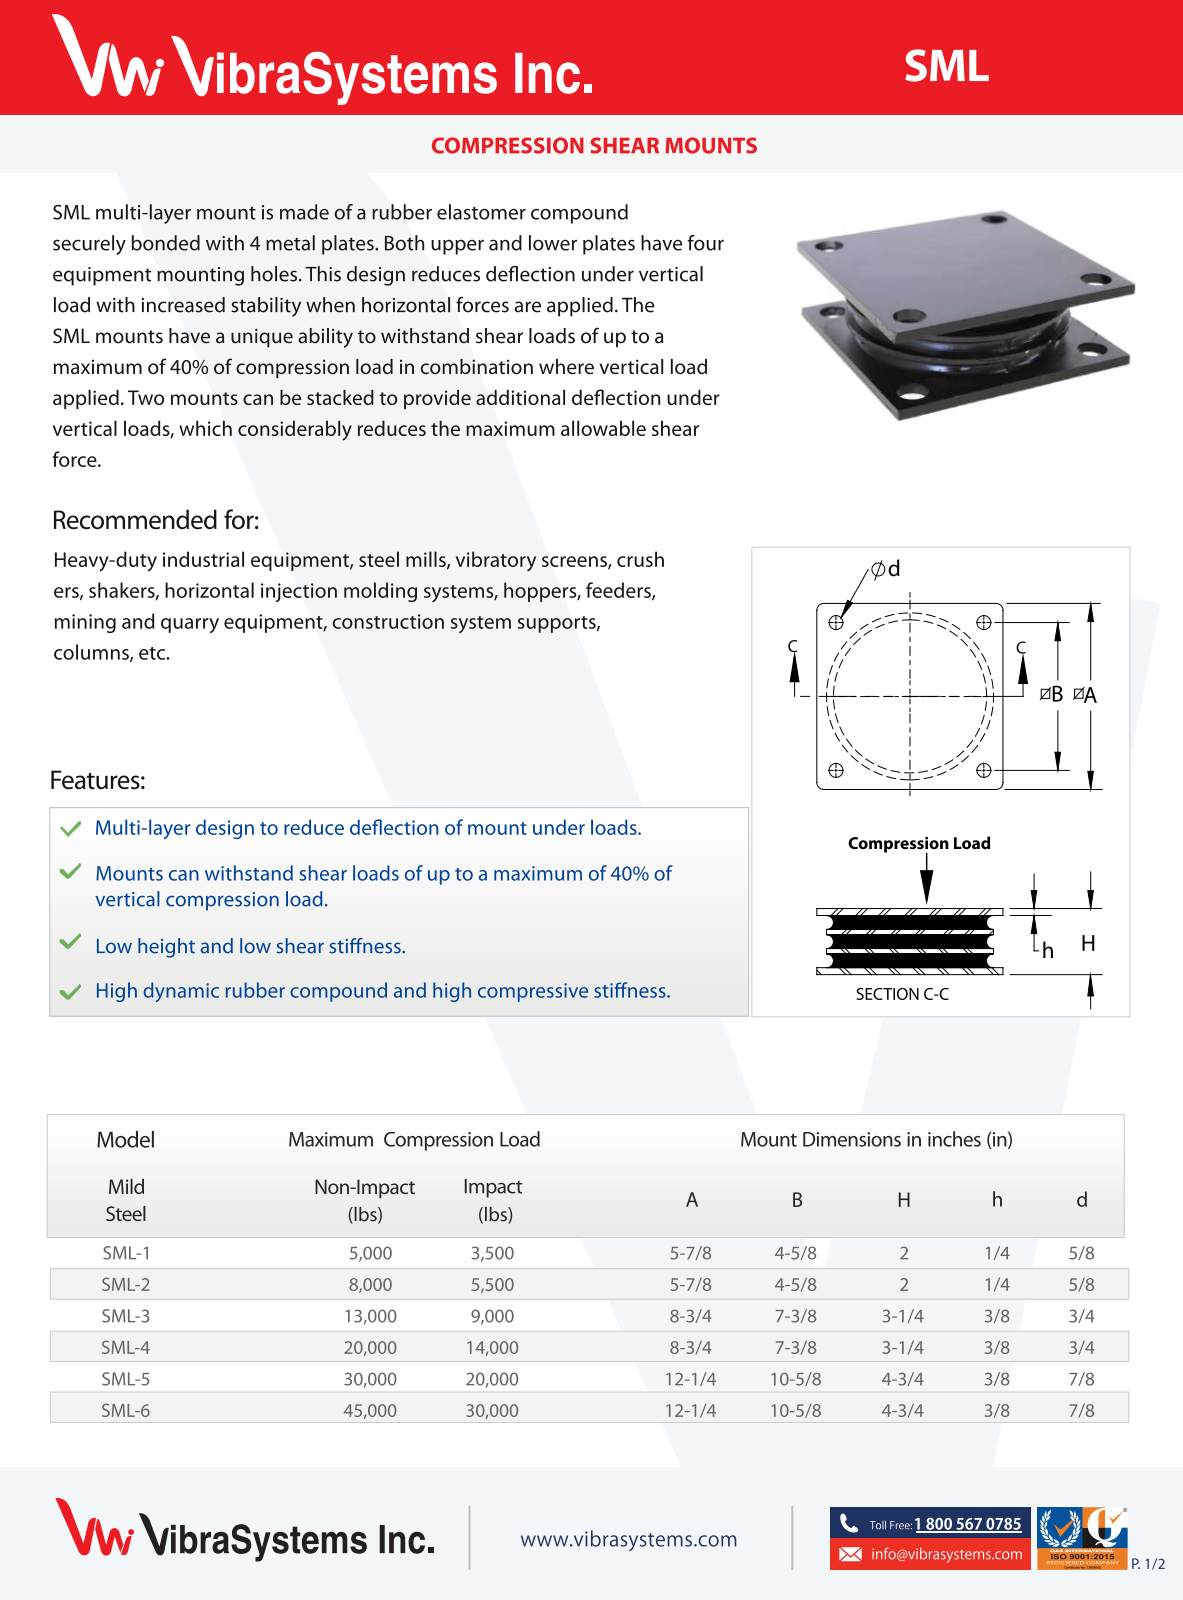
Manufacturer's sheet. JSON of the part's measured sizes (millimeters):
{"part_name": "SML-6 RevF", "step_written_by": "SolidWorks 2016 (CONFIG_CONTROL_DESIGN)", "units": "millimeters", "bodies": {"solids": 7, "faces": 54, "planar": 22, "cylindrical": 20, "other": 12}, "overall_size": [311.2, 311.2, 120.7], "volume_mm3": 7517000, "surface_area_mm2": 1204000, "round_holes": [[22.2, 4]], "round_bosses_or_shafts": [[298.5, 1]], "face_to_face_distances": [6.4, 35.8, 29.7, 36.1, 65.5, 71.9, 9.5, 39.2, 45.6, 75.1], "hole_center_spacings": [269.9, 381.7]}
